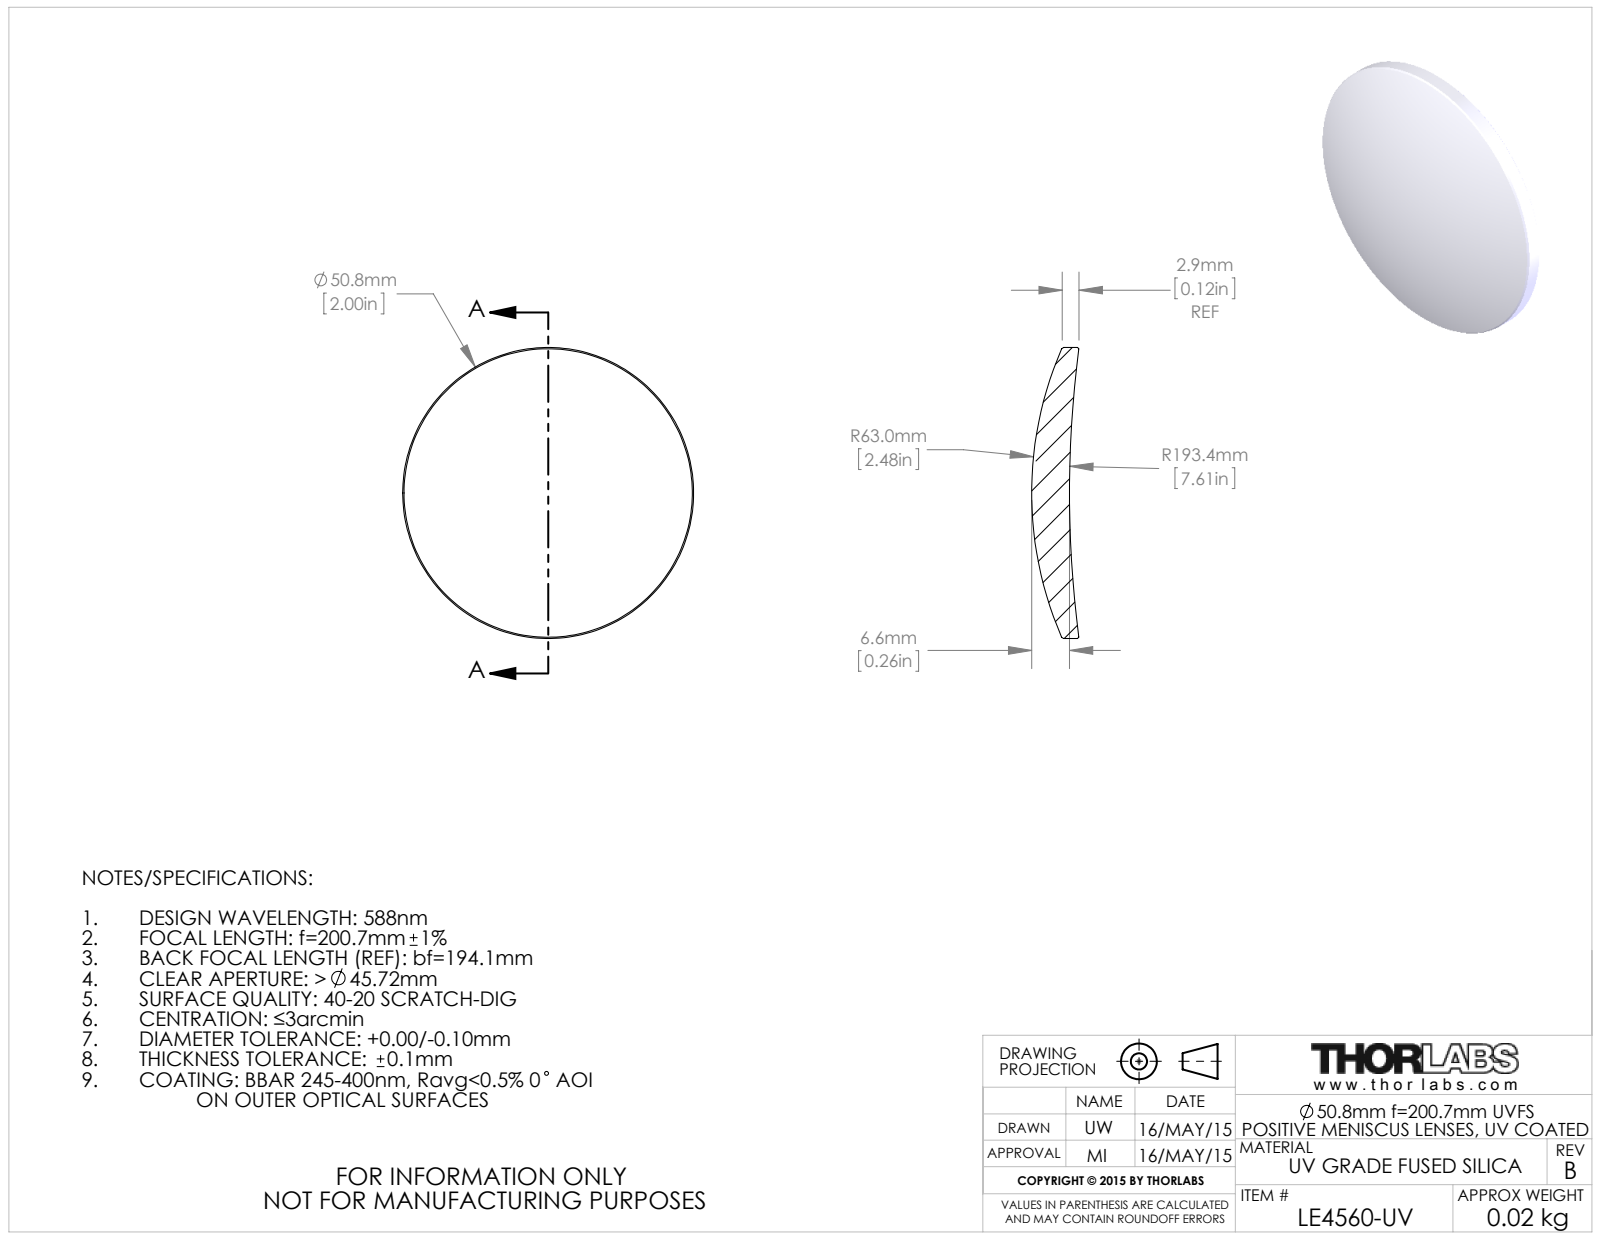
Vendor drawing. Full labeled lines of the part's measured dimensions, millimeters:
Part name (STEP PRODUCT): 4933-E0W
STEP written by: SolidWorks 2014 (CONFIG_CONTROL_DESIGN)
Units: millimetres
Bodies: 1 solid, 10 faces (0 planar, 2 cylindrical, 8 other)
Overall size (bounding box): 50.8 × 50.8 × 8.24
Volume: 9 724 mm³ · Surface area: 4 579 mm²
Round bosses / shafts (diameter × count): ⌀50.8 ×1
